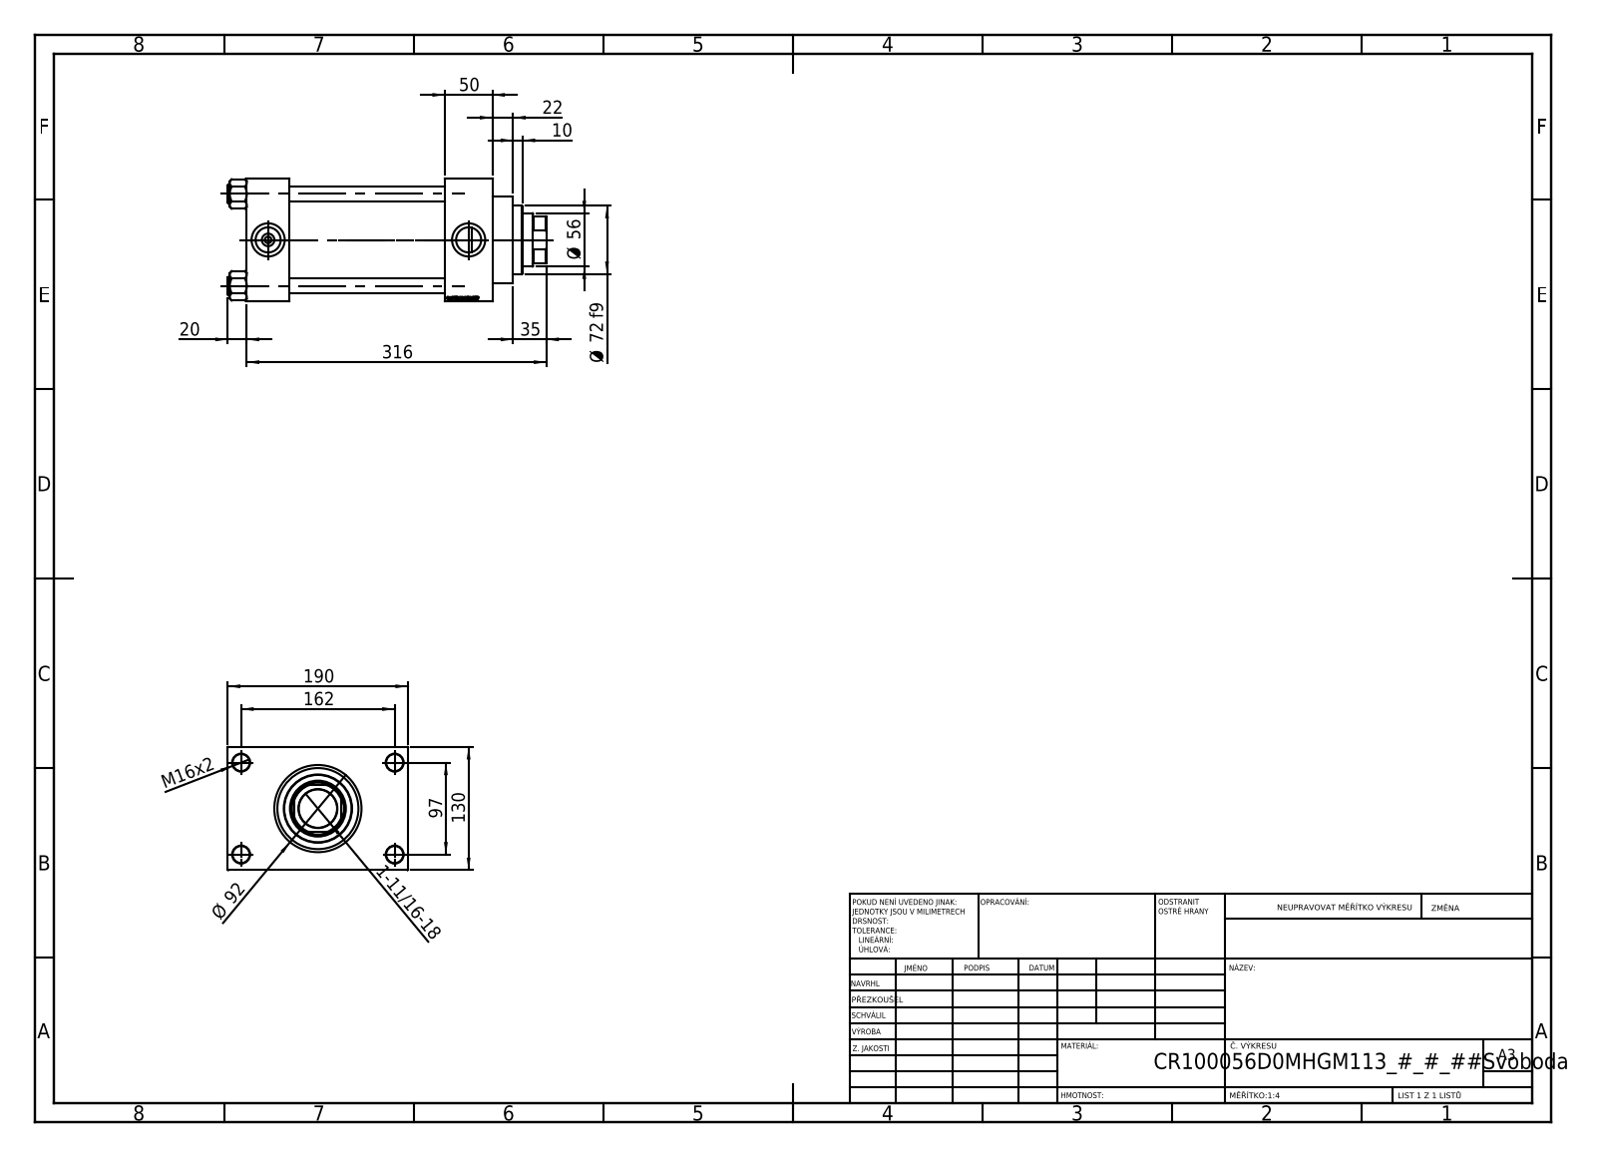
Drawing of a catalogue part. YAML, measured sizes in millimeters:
part_name: "V215CR_D_TYCINKA; V215_VC_A; V215CR_VCP_D; V215CR_D_Body (+1 more)"
step_written_by: "SolidWorks 2019 (CONFIG_CONTROL_DESIGN)"
units: millimeters
bodies: {solids: 11, faces: 1151, planar: 545, cylindrical: 88, other: 518}
overall_size: [336, 190, 130]
volume: 3022000
surface_area: 457610
round_holes:
  - {diameter: 16, count: 4}
  - {diameter: 18, count: 4}
  - {diameter: 7, count: 2}
  - {diameter: 26.44, count: 2}
  - {diameter: 35, count: 2}
  - {diameter: 40.5, count: 1}
  - {diameter: 56, count: 1}
  - {diameter: 59, count: 1}
  - {diameter: 76, count: 1}
  - {diameter: 85.5, count: 1}
  - {diameter: 100, count: 1}
round_bosses_or_shafts:
  - {diameter: 19, count: 4}
  - {diameter: 106, count: 1}
  - {diameter: 92, count: 1}
  - {diameter: 72, count: 1}
partial_cylinders:
  - {radius: 27, count: 1}
face_to_face_distances: [130, 50, 45, 209, 164, 259, 214, 30, 160, 190]
hole_center_spacings: [32.55, 68.52, 94.41, 96.9, 102.27, 129.45, 161.73, 97]
